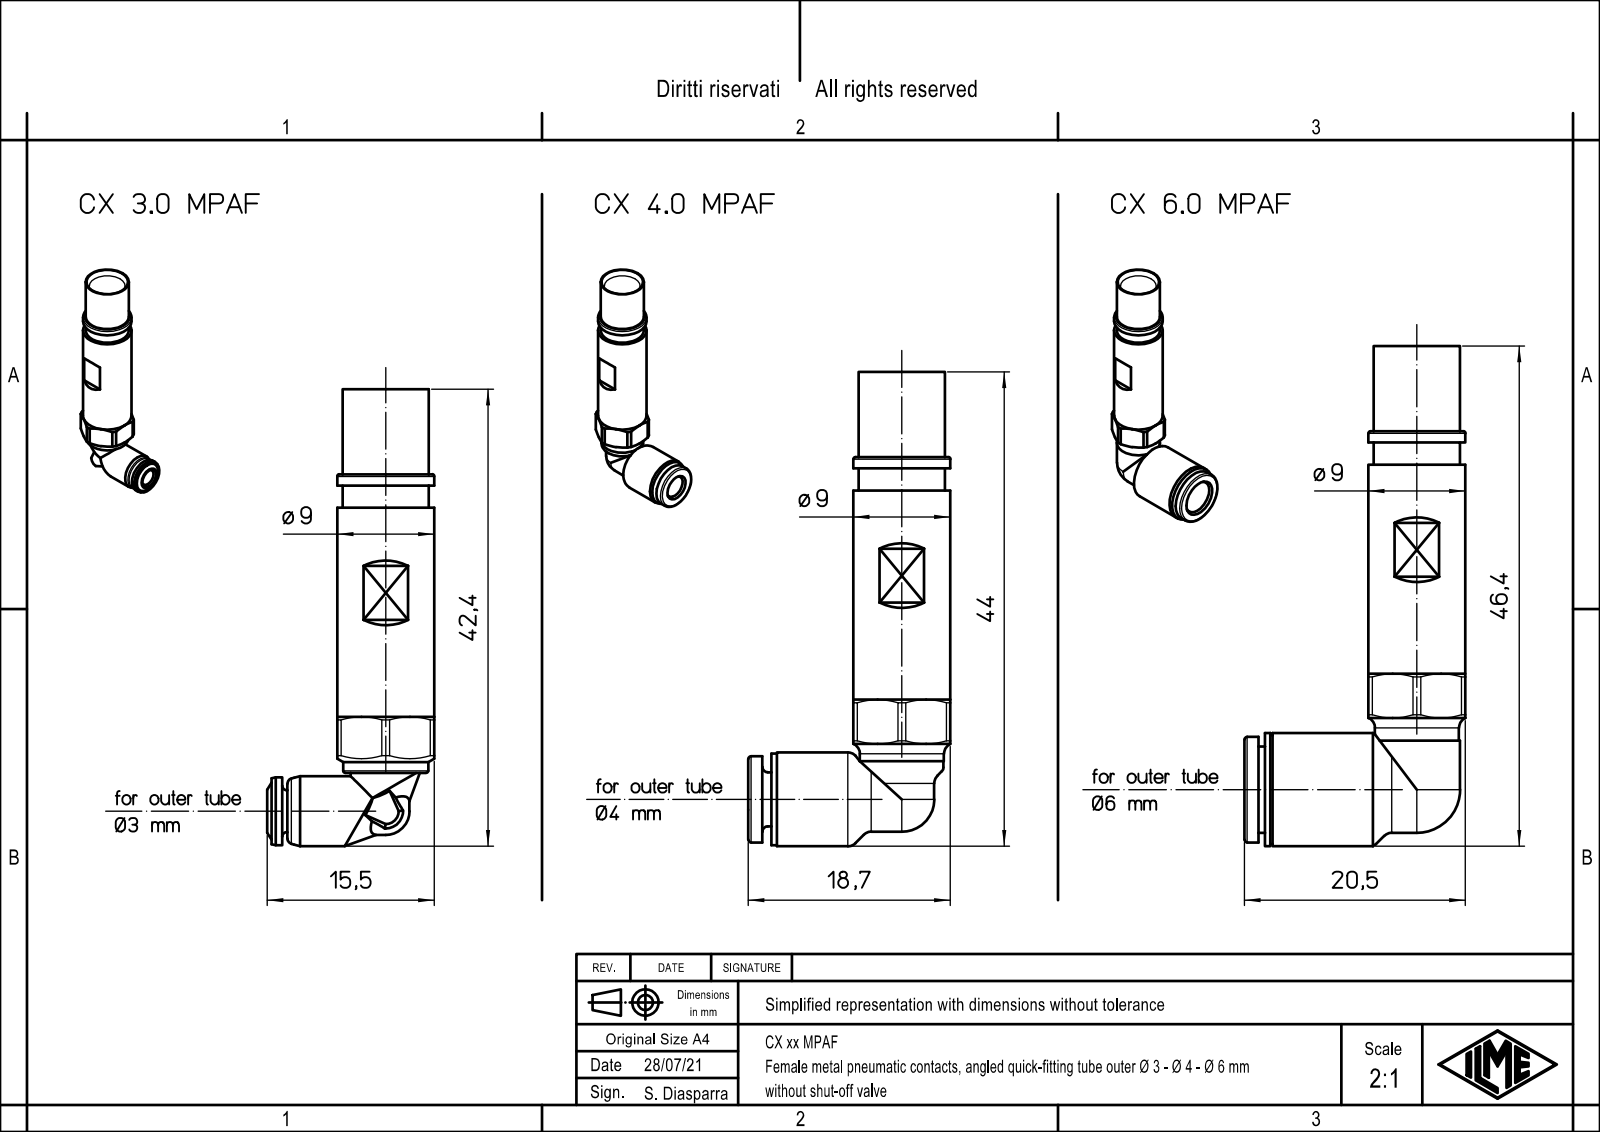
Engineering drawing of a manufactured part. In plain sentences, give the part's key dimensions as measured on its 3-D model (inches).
The part is named "CX_6.0_MPAF". Its 3-D file was written by "Creo Elements/Direct Modeling 20.1B 02-Apr-2019 (C) Parametric Technology GmbH (AUTOMOTIVE_DESIGN)". It is 1 solid with 137 faces: 43 planar, 42 cylindrical and 52 other. Overall it measures 1.827 by 0.807 by 0.413 inches. Its volume is 0.161 cubic inches and its surface area 3.996 square inches. Round holes: 1 of diameter 0.118, 1 of diameter 0.157, 1 of diameter 0.244, 1 of diameter 0.26. Round bosses or shafts: 2 of diameter 0.315, 1 of diameter 0.413, 1 of diameter 0.398, 1 of diameter 0.386, 1 of diameter 0.354, 1 of diameter 0.307. Partial cylindrical surfaces (rounded edges, fillets, slot ends): 1 of radius 0.006, 1 of radius 0.006, 1 of radius 0.007, 1 of radius 0.011, 1 of radius 0.02, 1 of radius 0.021, 1 of radius 0.197. The main face-to-face distances are 0.354, 0.051, 0.075, 0.452, 0.378, 0.024, 0.401, 0.315, 0.453, 0.402.
